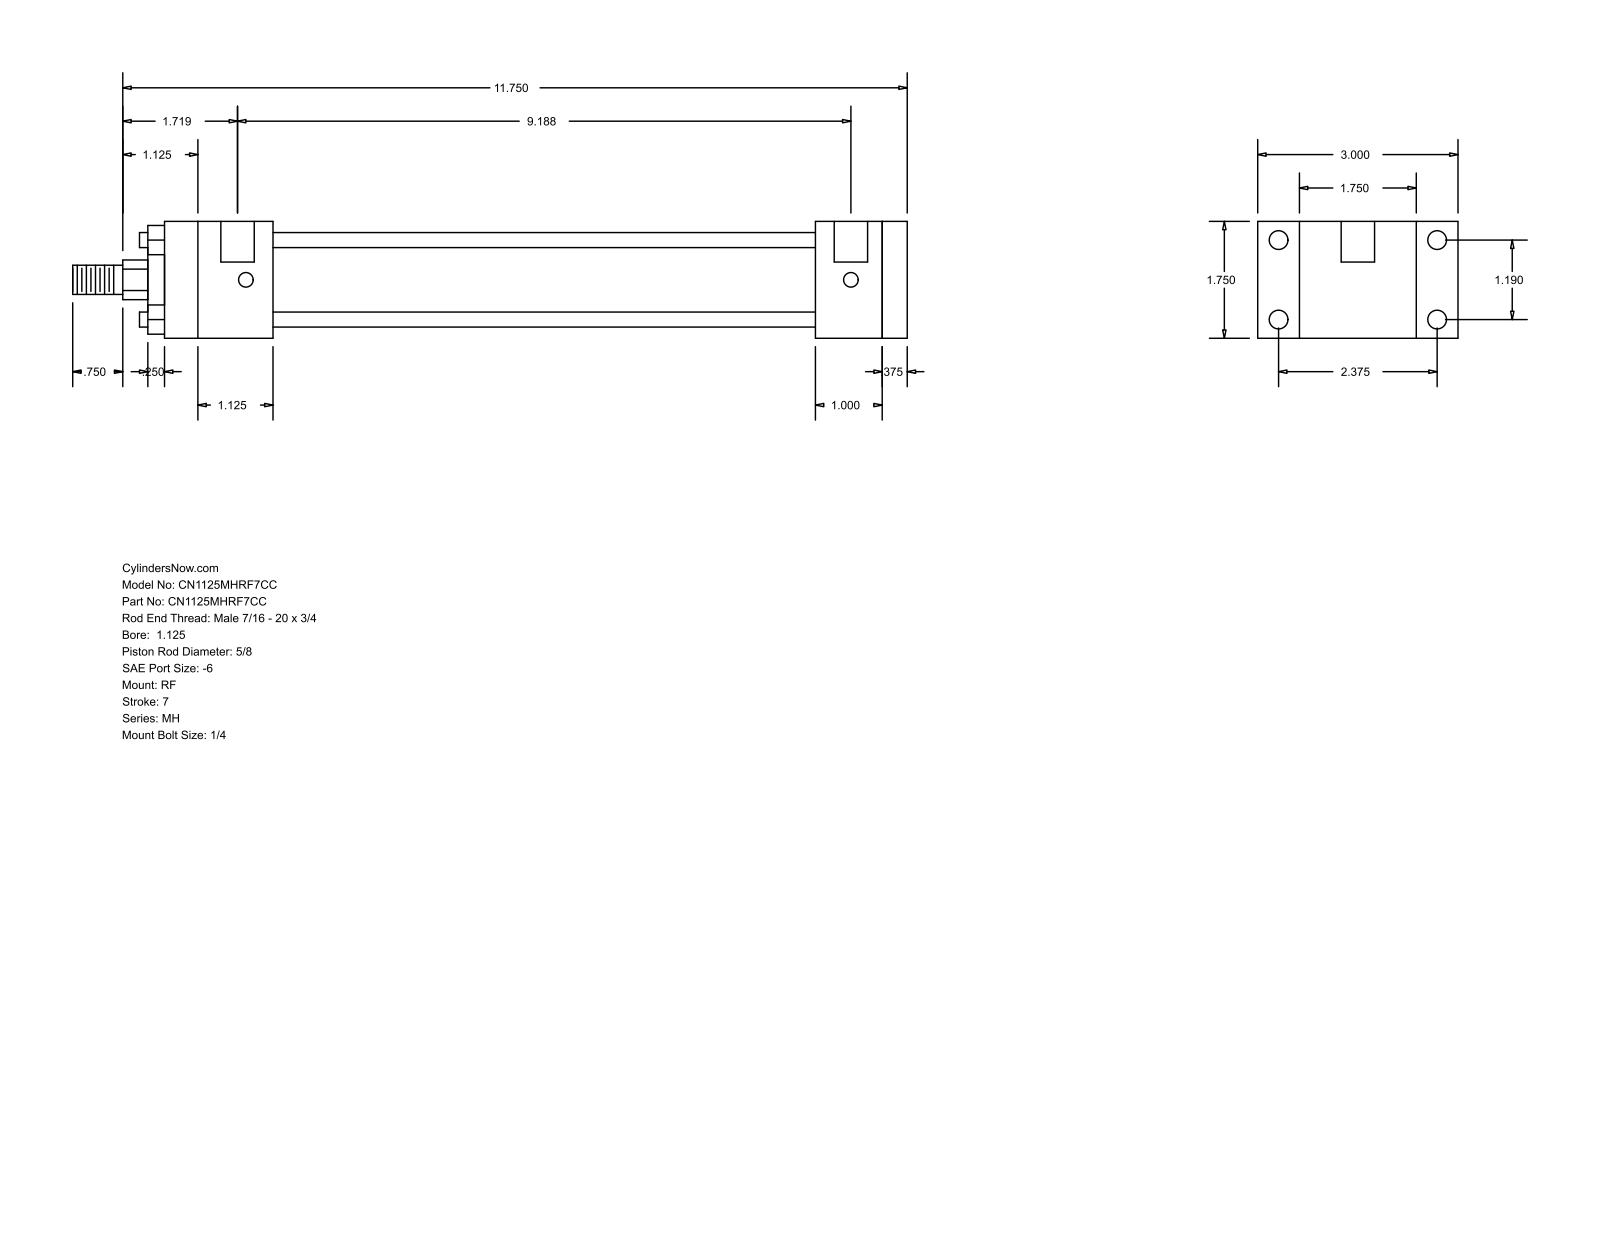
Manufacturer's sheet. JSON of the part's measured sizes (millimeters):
{"part_name": "MH_RF__0112_0.625", "step_written_by": "GSSL Pune (CONFIG_CONTROL_DESIGN)", "units": "millimeters", "bodies": {"solids": 0, "faces": 92, "planar": 64, "cylindrical": 28, "other": 0}, "overall_size": [317.5, 76.2, 44.45], "round_holes": [[5.56, 4], [7.14, 4], [12.7, 2]], "round_bosses_or_shafts": [[5.71, 4], [34.92, 1], [28.57, 1], [15.88, 1], [11.11, 1]], "partial_cylinders_radius": [[7.54, 1]], "face_to_face_distances": [44.46, 9.52, 34.93, 282.57, 15.87, 231.78, 241.3, 206.37, 25.41, 41.27], "hole_center_spacings": [30.22, 60.32, 67.47, 230.19, 3.17, 233.36]}
